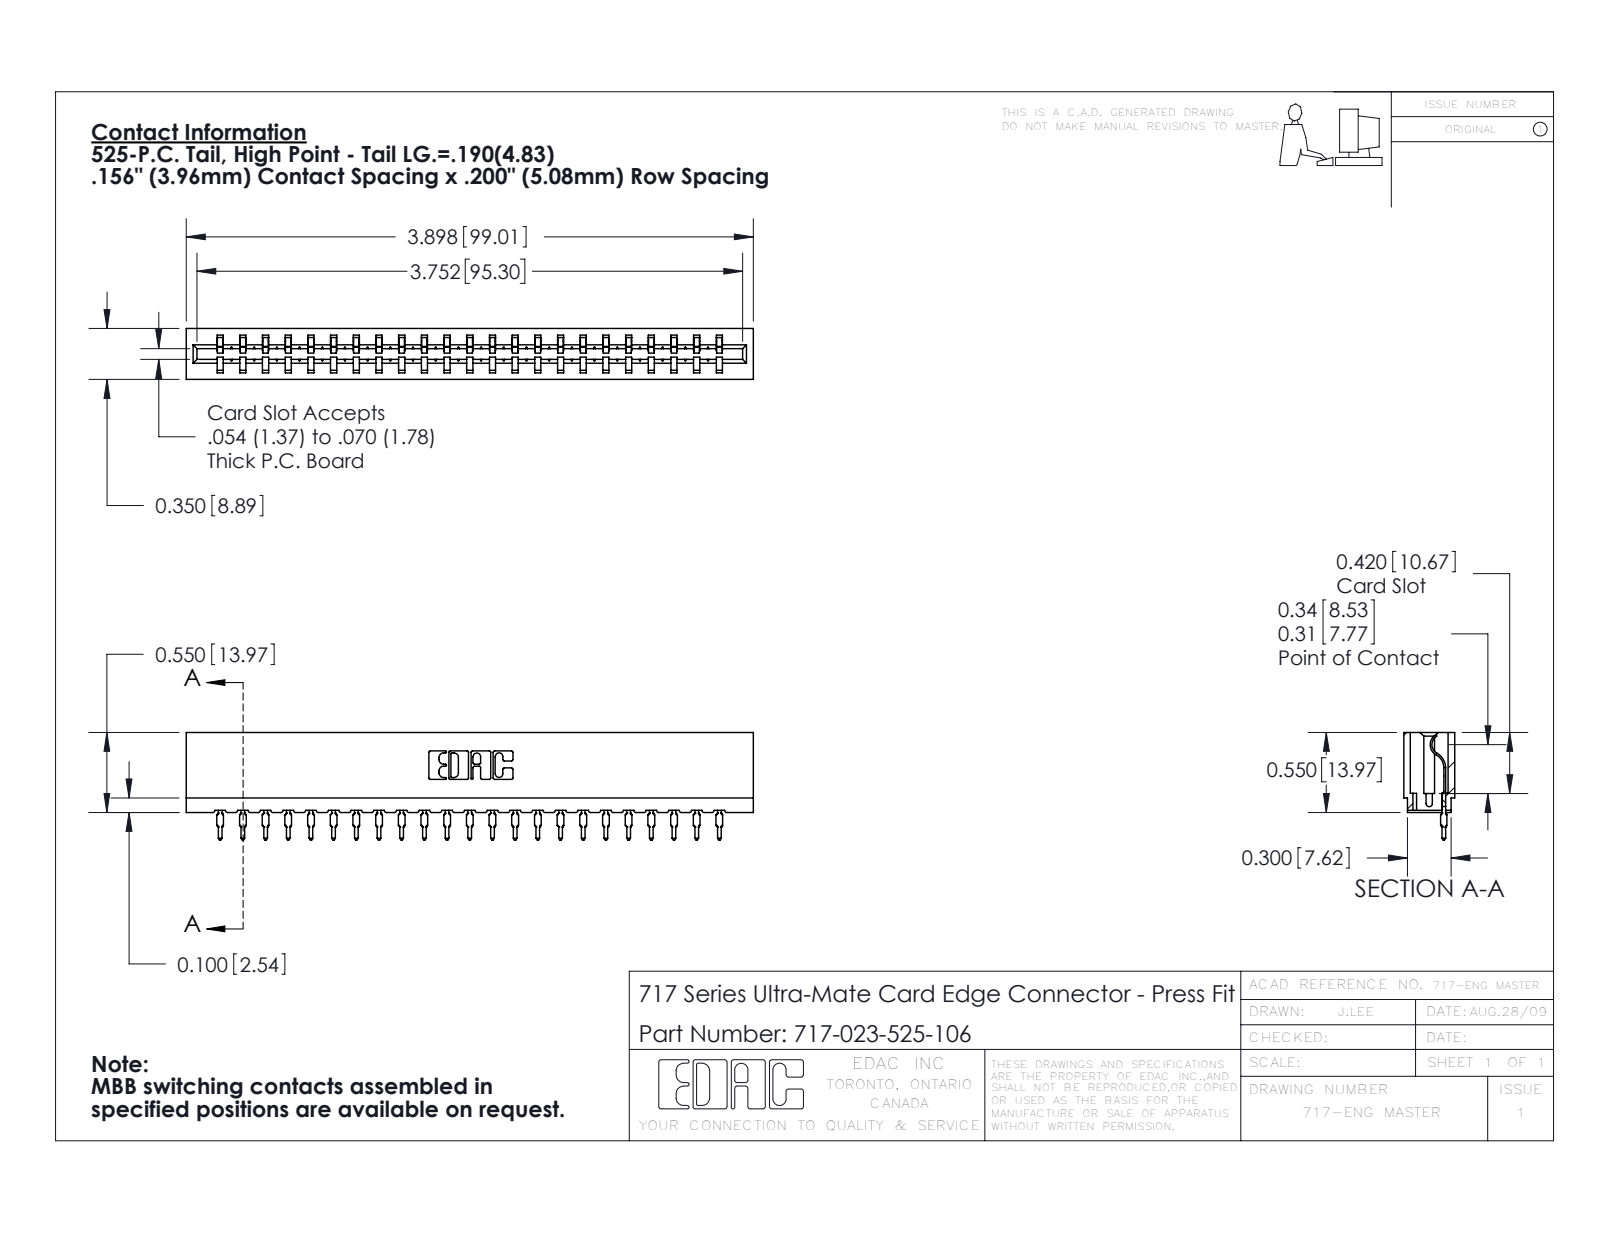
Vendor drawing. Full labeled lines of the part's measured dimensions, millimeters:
Part name (STEP PRODUCT): 717-023-525-106; 717 Part_Insulator Option - 06; 745-292-001_525
STEP written by: SolidWorks 2016 (CONFIG_CONTROL_DESIGN)
Units: millimetres
Bodies: 24 solids, 2693 faces (1618 planar, 477 cylindrical, 598 other)
Overall size (bounding box): 99 × 18.8 × 8.9
Volume: 8 420 mm³ · Surface area: 11 560 mm²
Partial cylindrical surfaces — rounded edges, fillets, slot ends (radius × count): R0.4 ×46, R0.5 ×46, R0.3 ×22, R0.2 ×6, R0.8 ×6, R0.1 ×4, R0.3 ×4, R0.7 ×3
Main face-to-face distances: 5.4, 3.5, 8.9, 4, 1.9, 15.8, 1.1, 0.6, 7.7, 2.4
